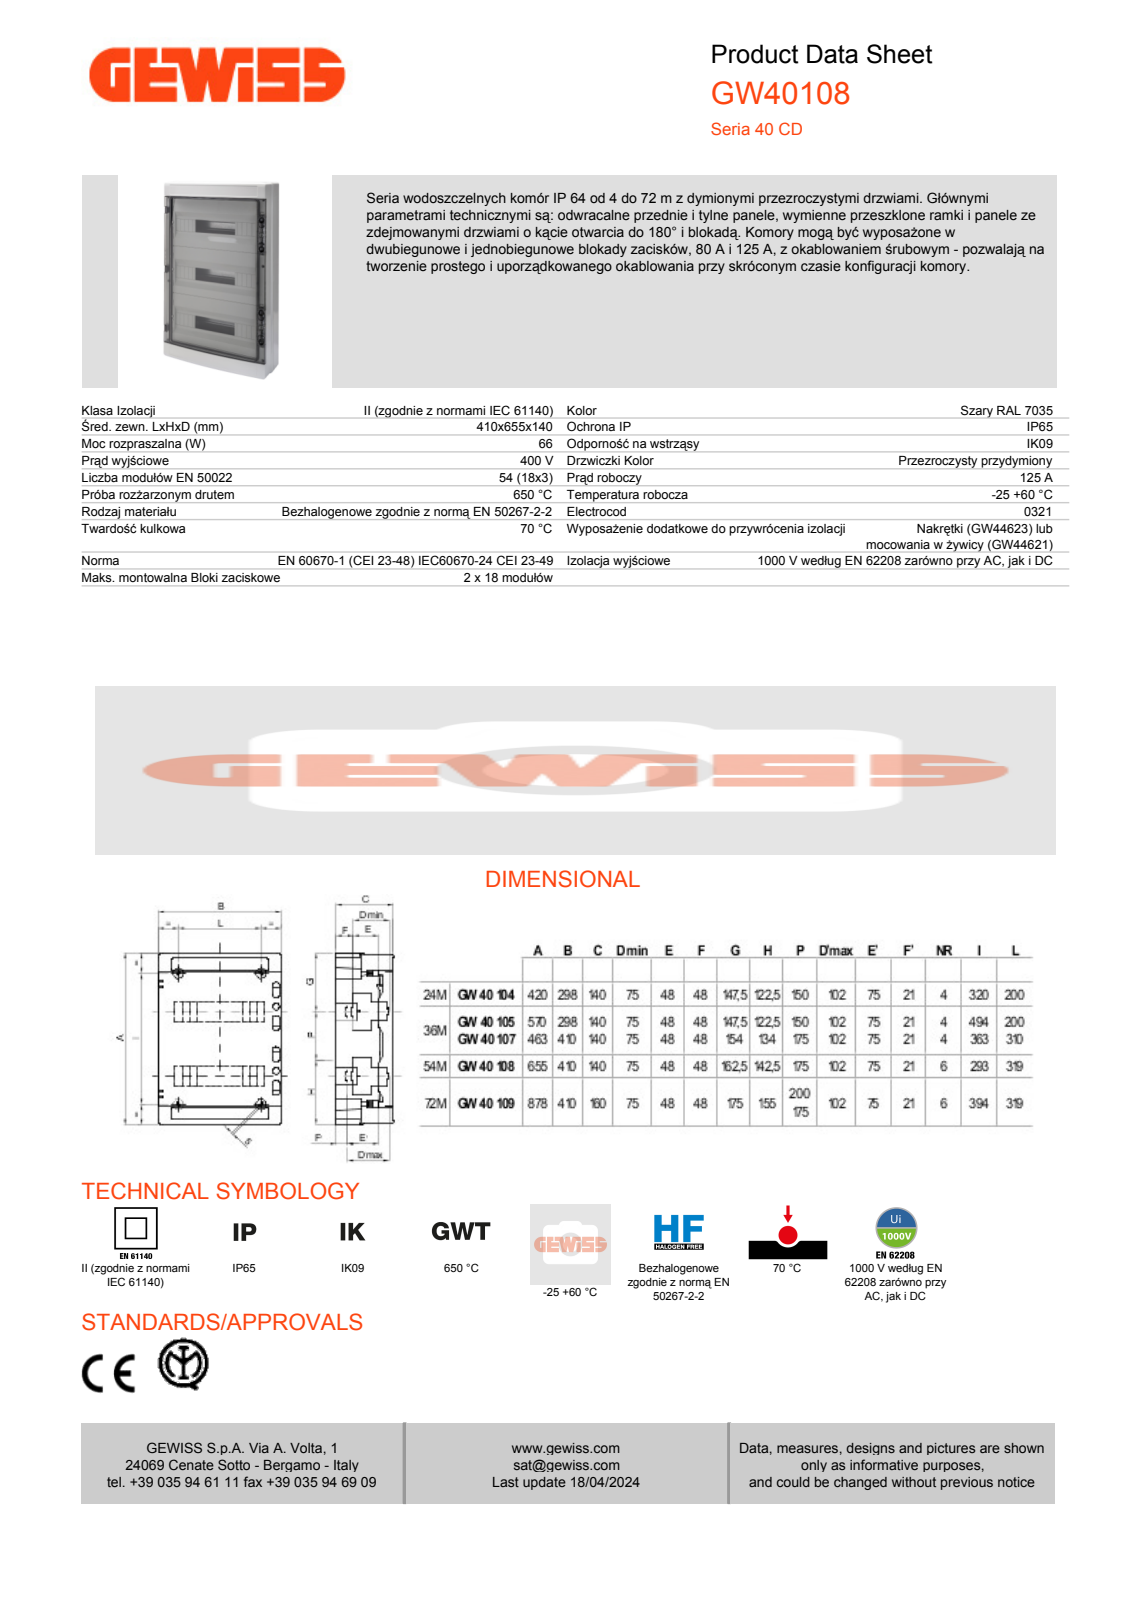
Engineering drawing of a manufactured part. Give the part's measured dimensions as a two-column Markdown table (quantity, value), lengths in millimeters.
| quantity | value |
| --- | --- |
| part name | GW_40_108_SCATOLA_OR; GW_40_108_COPERCHIO_OR; GW40108_COMPONENTE_PLASTICA_DX; GW40108_COMPONENTE_PLASTICA_SX (+2 more) |
| STEP written by | CREO PARAMETRIC BY PTC INC, 2020354 (CONFIG_CONTROL_DESIGN) |
| units | millimeters |
| bodies | 7 solids, 1708 faces (1283 planar, 320 cylindrical, 105 other) |
| overall size | 655 × 410 × 148.88 |
| volume | 10 610 000 mm³ |
| surface area | 2 067 000 mm² |
| round holes (diameter × count) | 3.2 × 12, 6 × 6, 21 × 6, 8.5 × 4, 4.2 × 3 |
| round bosses / shafts (diameter × count) | 25 × 6, 10 × 6 |
| partial cylindrical surfaces (radius × count) | 4.5 × 16, 10 × 16, 0.8 × 12, 1.8 × 12, 2.1 × 12, 4 × 12, 5 × 10, 3.2 × 8 |
| main face-to-face distances | 3.5, 4, 7.5, 104, 100.5, 113, 109.5, 9, 406, 402 |
| hole center spacings | 174.54, 393.43, 24.25, 17.6, 330.12, 352.6, 353.04, 39.47 |
